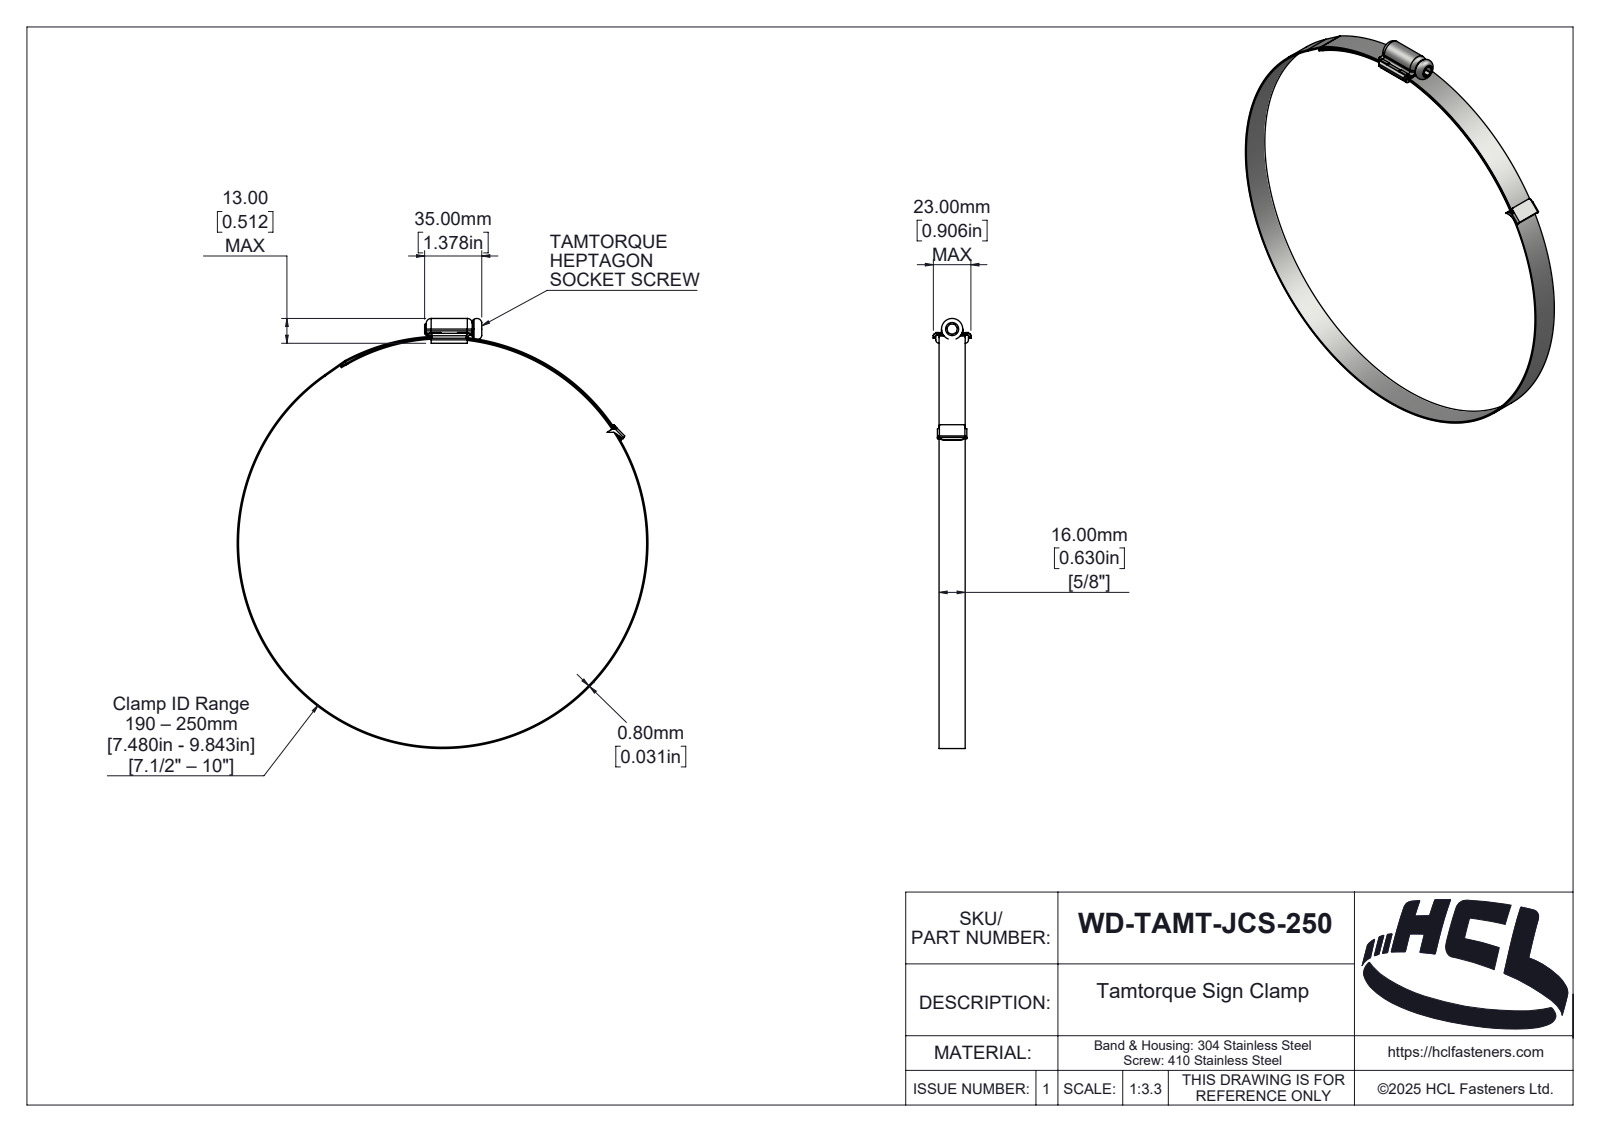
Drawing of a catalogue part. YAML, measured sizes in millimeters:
part_name: "WD-TAMT-JCS-250"
step_written_by: "SolidWorks 2025 (AUTOMOTIVE_DESIGN)"
units: millimeters
bodies: {solids: 5, faces: 321, planar: 101, cylindrical: 139, other: 81}
overall_size: [263.3, 251.6, 23]
volume: 18056
surface_area: 38585
round_holes:
  - {diameter: 6, count: 1}
  - {diameter: 250, count: 1}
round_bosses_or_shafts:
  - {diameter: 251.6, count: 1}
  - {diameter: 9, count: 1}
  - {diameter: 5.8, count: 1}
partial_cylinders:
  - {radius: 0.1, count: 28}
  - {radius: 1, count: 10}
  - {radius: 0.5, count: 7}
  - {radius: 3, count: 6}
  - {radius: 1.5, count: 4}
  - {radius: 1.2, count: 2}
  - {radius: 2.1, count: 2}
  - {radius: 0.46, count: 1}
face_to_face_distances: [16, 2, 4.9, 2.9, 18, 0.8, 1, 3.5, 3, 0.5]
